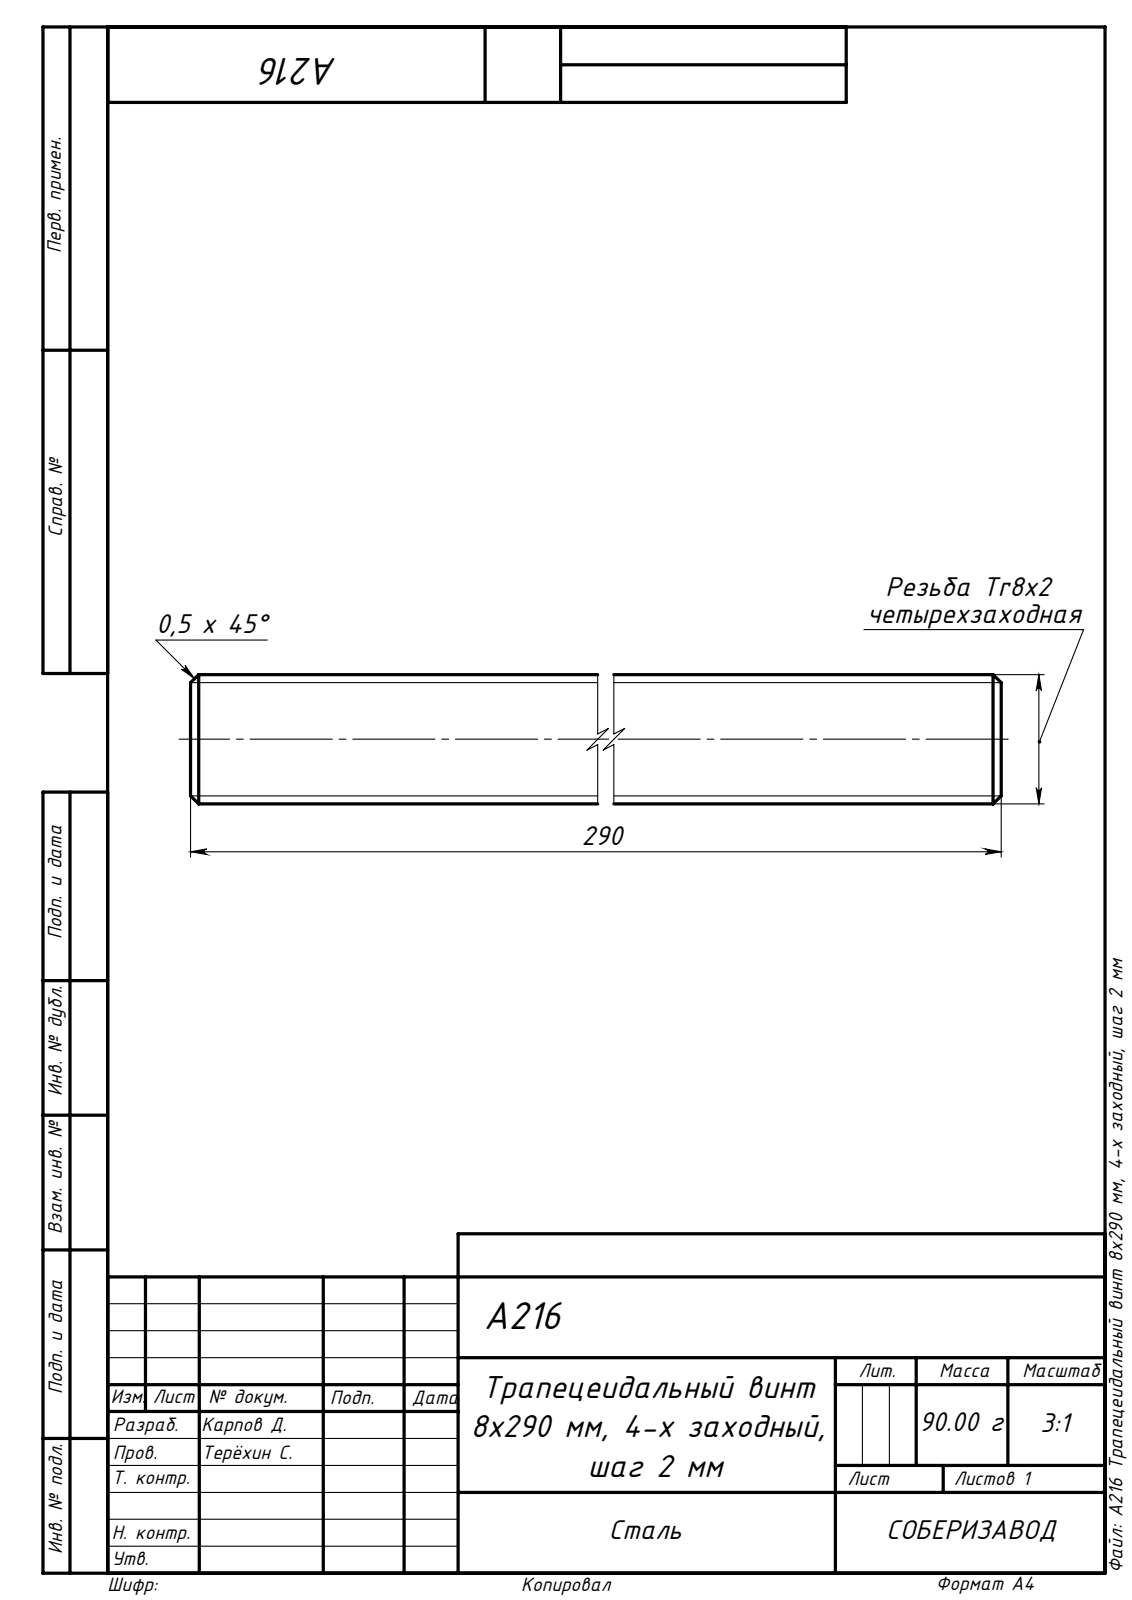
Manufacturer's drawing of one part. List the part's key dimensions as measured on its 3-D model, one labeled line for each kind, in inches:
Part name (STEP PRODUCT): A216 Трапецеидальный винт 8х290 мм, 4-х заходный, шаг 2 мм
STEP written by: SolidWorks 2018 (AUTOMOTIVE_DESIGN)
Units: inches
Bodies: 1 solid, 4 faces (2 planar, 2 cylindrical, 0 other)
Overall size (bounding box): 11.417 × 0.315 × 0.315
Volume: 0.89 in³ · Surface area: 11.45 in²
Round bosses / shafts (diameter × count): ⌀0.315 ×1
Main face-to-face distances: 11.417
